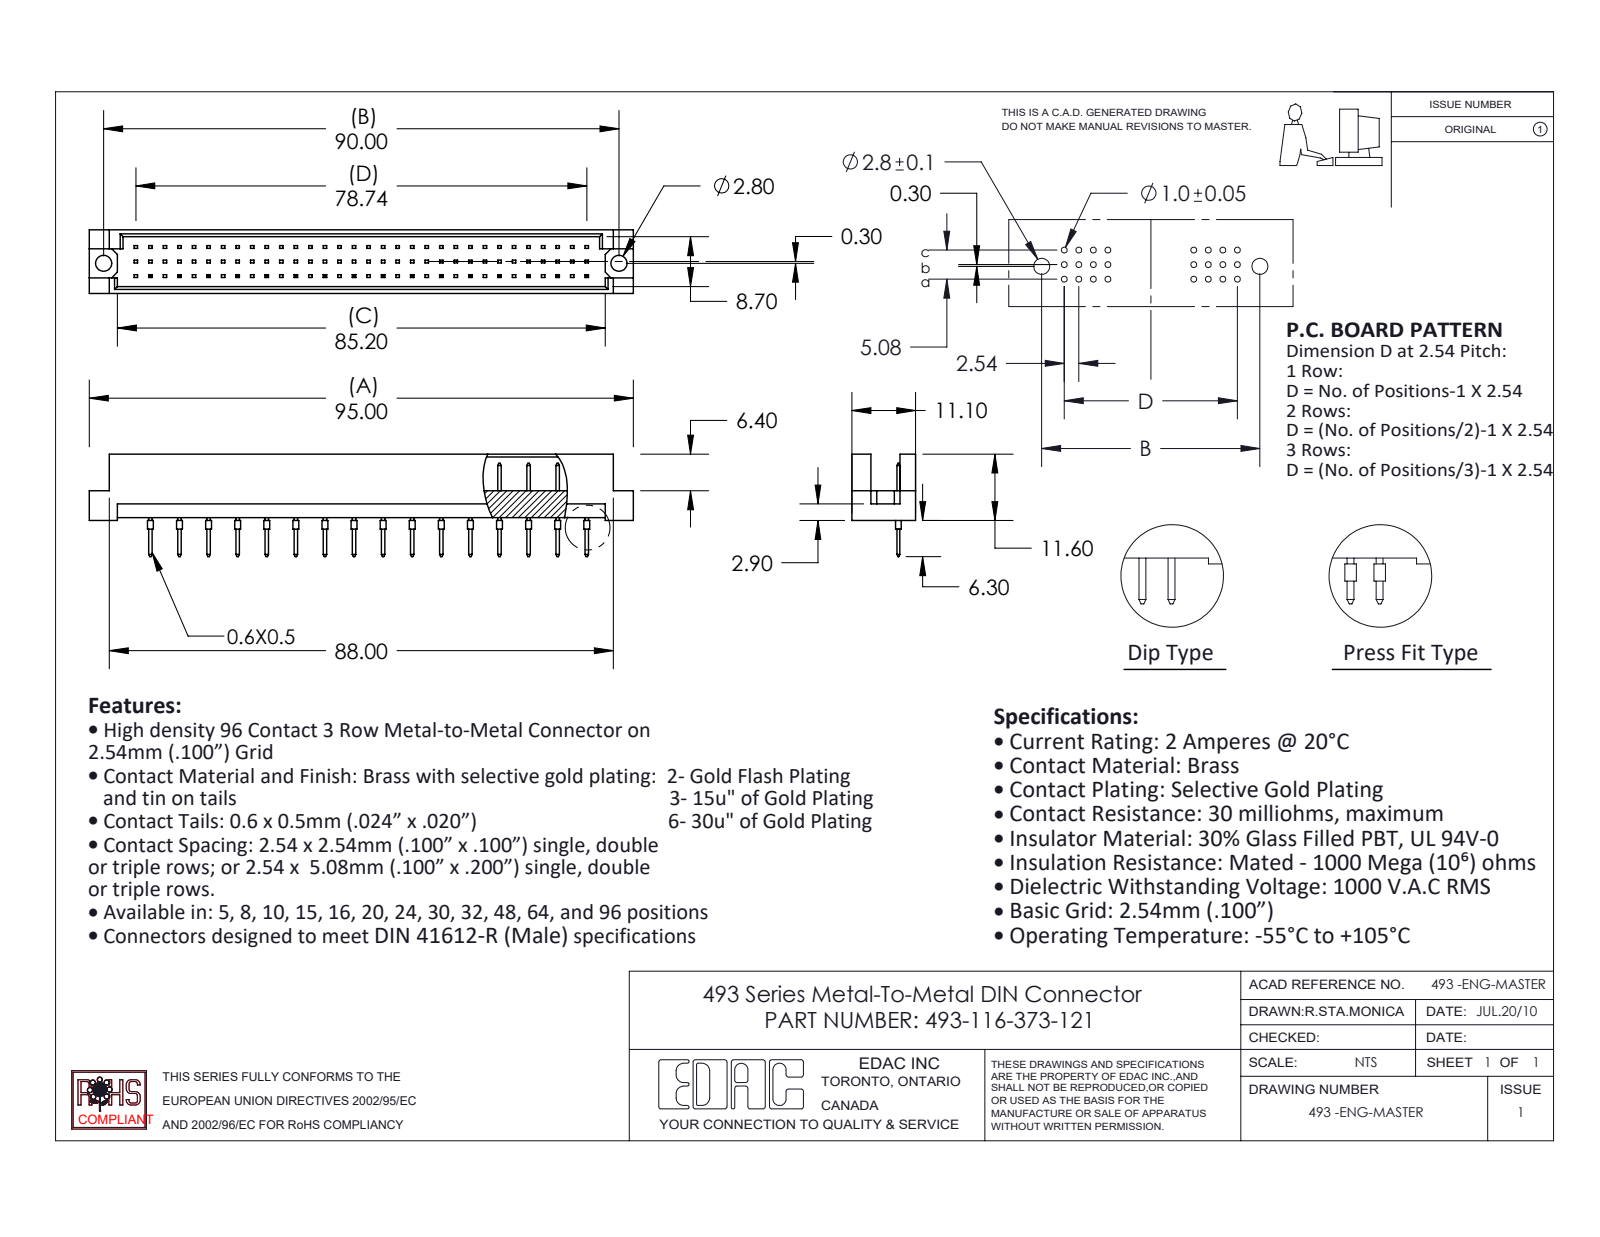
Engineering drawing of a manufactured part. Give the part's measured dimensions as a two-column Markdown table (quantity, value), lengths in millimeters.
| quantity | value |
| --- | --- |
| part name | 493-116-373-121; 493 Part_96; 493-290_73 |
| STEP written by | SolidWorks 2020 (CONFIG_CONTROL_DESIGN) |
| units | millimeters |
| bodies | 17 solids, 788 faces (752 planar, 36 cylindrical, 0 other) |
| overall size | 95 × 17.9 × 11.1 |
| volume | 5 747 mm³ |
| surface area | 7 080 mm² |
| round holes (diameter × count) | 2.8 × 2 |
| round bosses / shafts (diameter × count) | 1 × 16 |
| main face-to-face distances | 1.2, 9.9, 11.1, 8.7, 4.7, 0.5, 5.08, 2.54, 2.76, 3.26 |
| hole center spacings | 90 |
